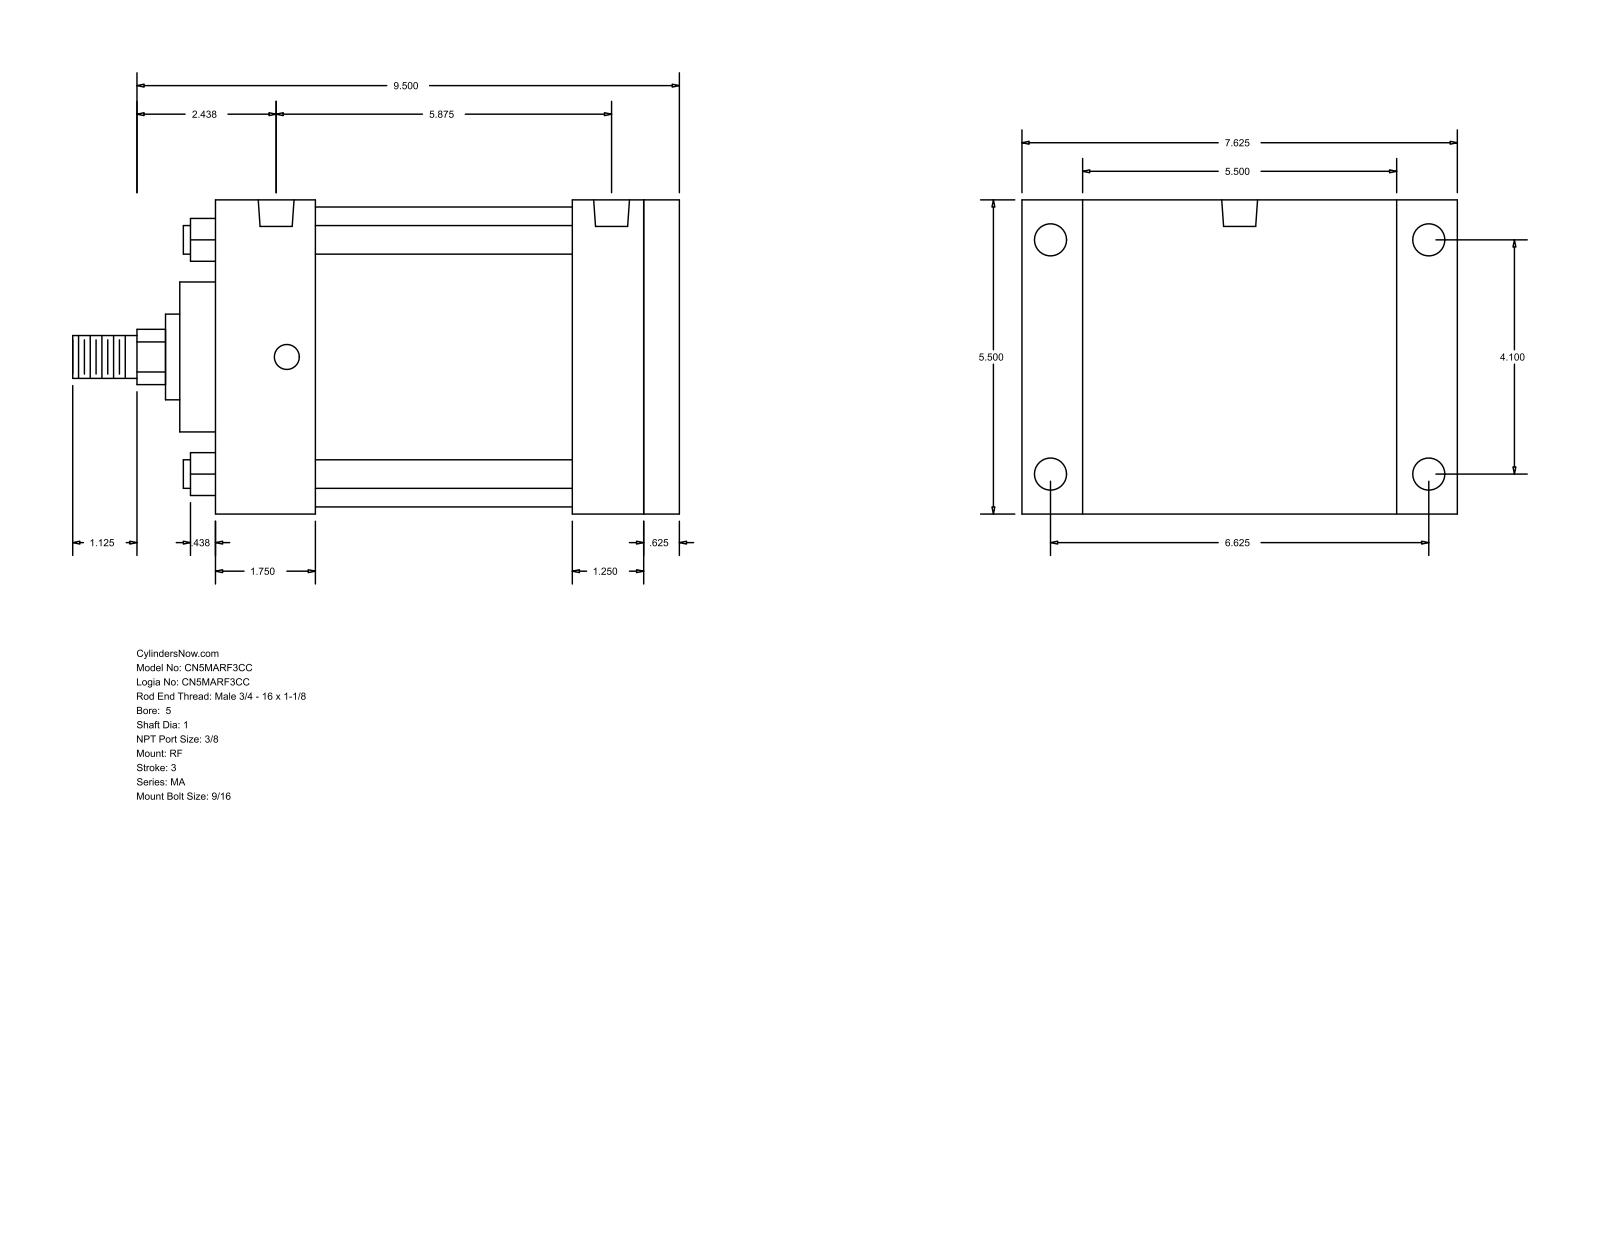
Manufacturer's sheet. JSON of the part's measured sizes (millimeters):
{"part_name": "MA_RF__0500_1", "step_written_by": "GSSL Pune (CONFIG_CONTROL_DESIGN)", "units": "millimeters", "bodies": {"solids": 0, "faces": 94, "planar": 65, "cylindrical": 29, "other": 0}, "overall_size": [269.88, 193.68, 139.7], "round_holes": [[11.11, 4], [14.29, 4], [15.93, 2]], "round_bosses_or_shafts": [[12.7, 4], [133.35, 1], [66.67, 1], [38.1, 1], [25.4, 1], [19.05, 1]], "partial_cylinders_radius": [[12.29, 1]], "face_to_face_distances": [139.7, 206.38, 15.87, 190.51, 47.62, 44.46, 146.05, 161.92, 158.76, 114.3], "hole_center_spacings": [4.76, 104.14, 139.71, 144.47, 168.28, 197.9, 149.23]}
